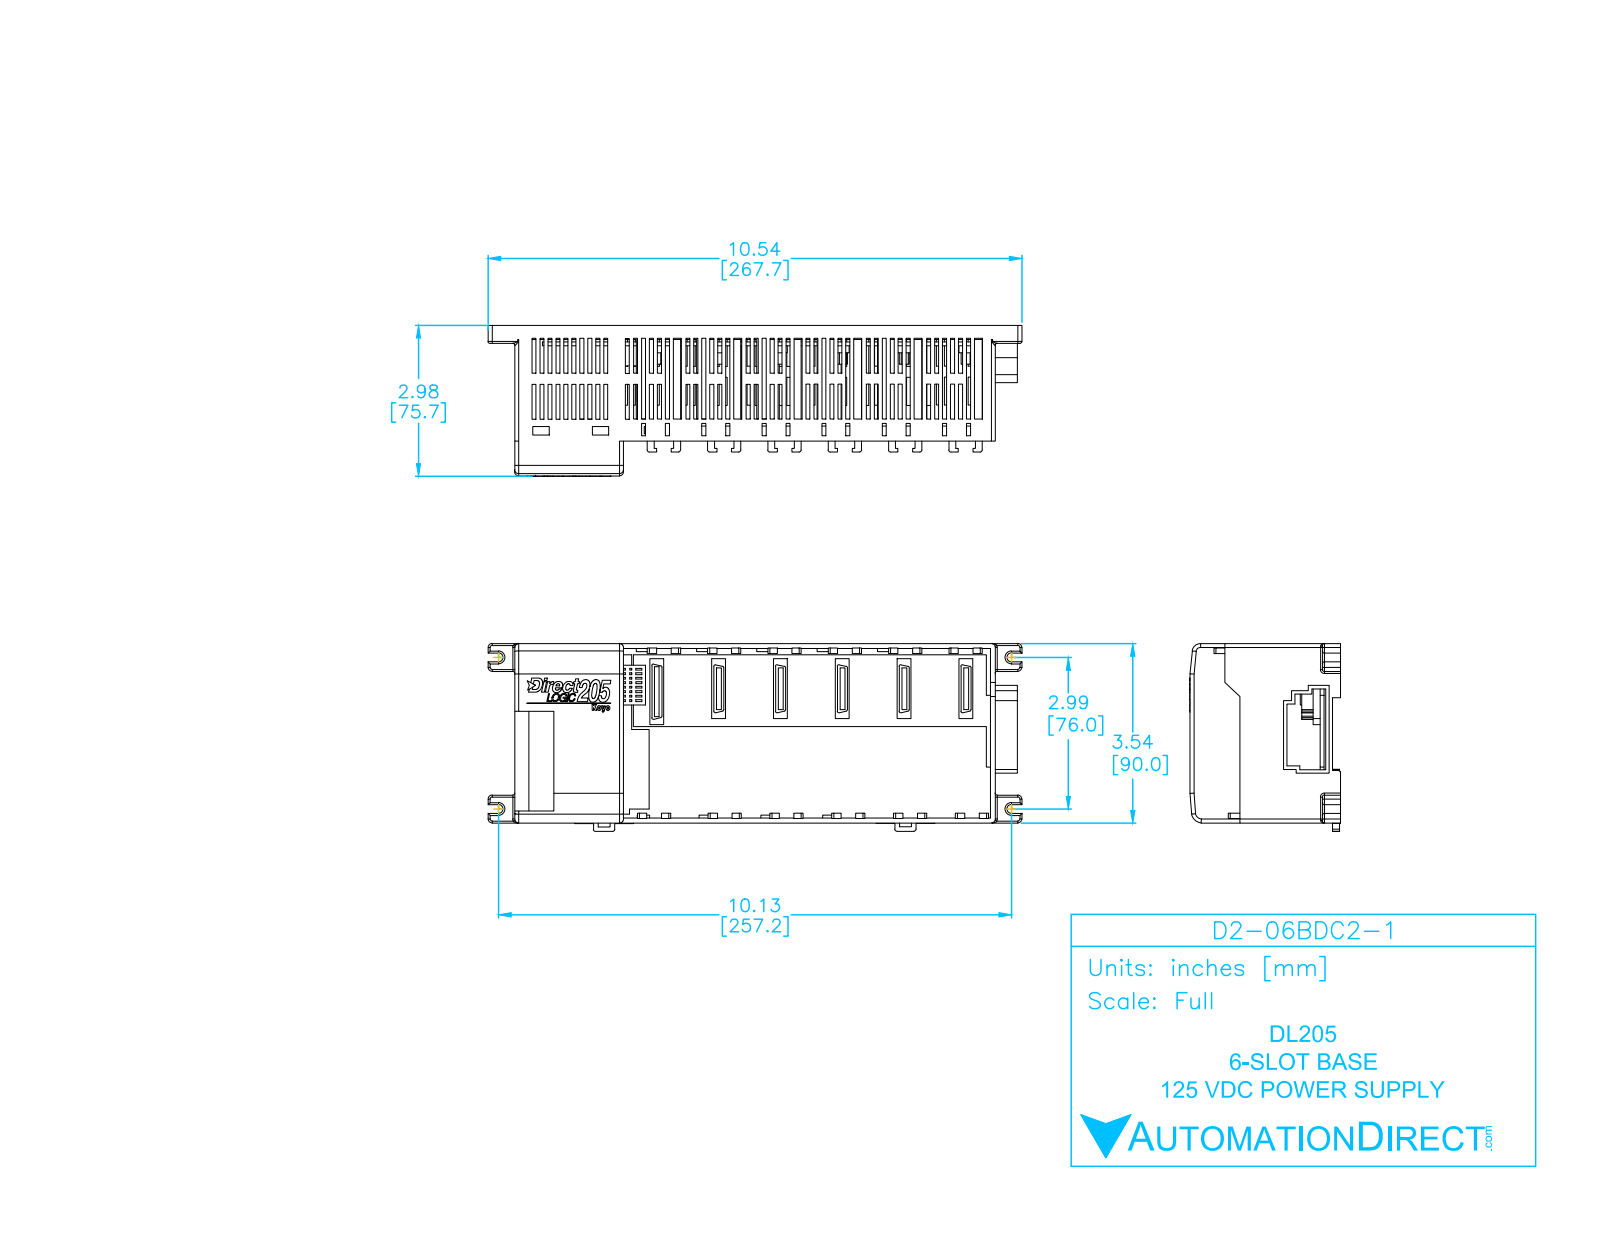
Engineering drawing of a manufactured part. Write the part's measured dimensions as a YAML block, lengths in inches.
part_name: "D2-06BDC2-1"
step_written_by: "SolidWorks 2009 (AUTOMOTIVE_DESIGN)"
units: inches
bodies: {solids: 6, faces: 2240, planar: 1903, cylindrical: 174, other: 163}
overall_size: [10.538, 3.709, 2.98]
volume: 17.67
surface_area: 297
round_bosses_or_shafts:
  - {diameter: 0.213, count: 6}
partial_cylinders:
  - {radius: 0.039, count: 64}
  - {radius: 0.03, count: 24}
  - {radius: 0.079, count: 20}
  - {radius: 0.01, count: 16}
  - {radius: 0.087, count: 4}
  - {radius: 0.185, count: 4}
  - {radius: 0.162, count: 1}
  - {radius: 0.208, count: 1}
face_to_face_distances: [0.098, 0.118, 0.049, 3.346, 3.445, 0.079, 0.167, 0.246, 0.128, 3.543]
